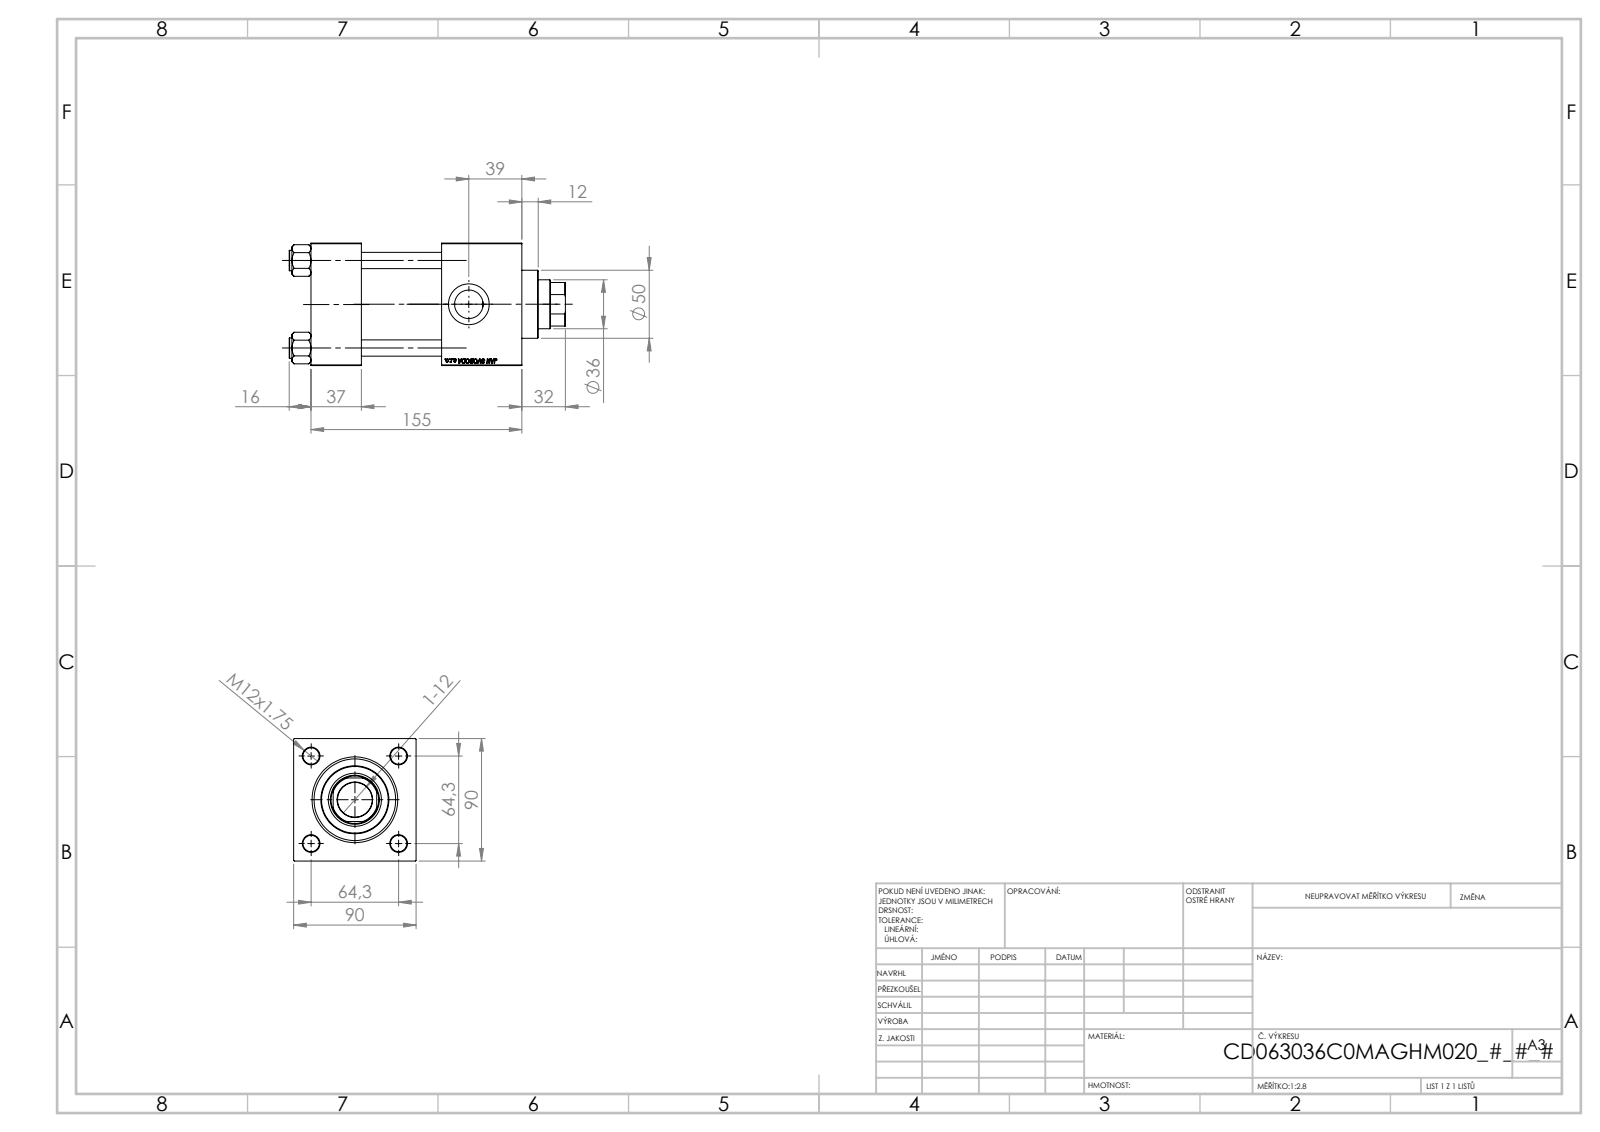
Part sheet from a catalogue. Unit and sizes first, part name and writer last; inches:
Units: inches
Overall size (bounding box): 7.992 × 3.543 × 3.543
Round holes (diameter × count): ⌀0.472 ×4, ⌀0.276 ×2, ⌀0.825 ×2, ⌀1.181 ×2, ⌀1.004 ×1, ⌀1.417 ×1, ⌀1.535 ×1, ⌀1.969 ×1, ⌀2.362 ×1, ⌀2.48 ×1
Round bosses / shafts (diameter × count): ⌀0.591 ×4, ⌀2.717 ×1
Partial cylindrical surfaces — rounded edges, fillets, slot ends (radius × count): R0.689 ×1
Main face-to-face distances: 3.543, 2.323, 1.457, 6.102, 4.646, 3.78, 4.972, 3.516, 1.193, 1.13
Hole centre spacings: 1.79, 2.531, 3.58
Volume: 59.06 in³ · Surface area: 285.6 in²
Bodies: 11 solids, 1149 faces (526 planar, 87 cylindrical, 536 other)
Part name (STEP PRODUCT): NUT_M5_V215CD_C; V215CD_C_TYCINKA; V215CD_VCP_C; V215CD_VC_C (+1 more)
STEP written by: SolidWorks 2019 (CONFIG_CONTROL_DESIGN)
